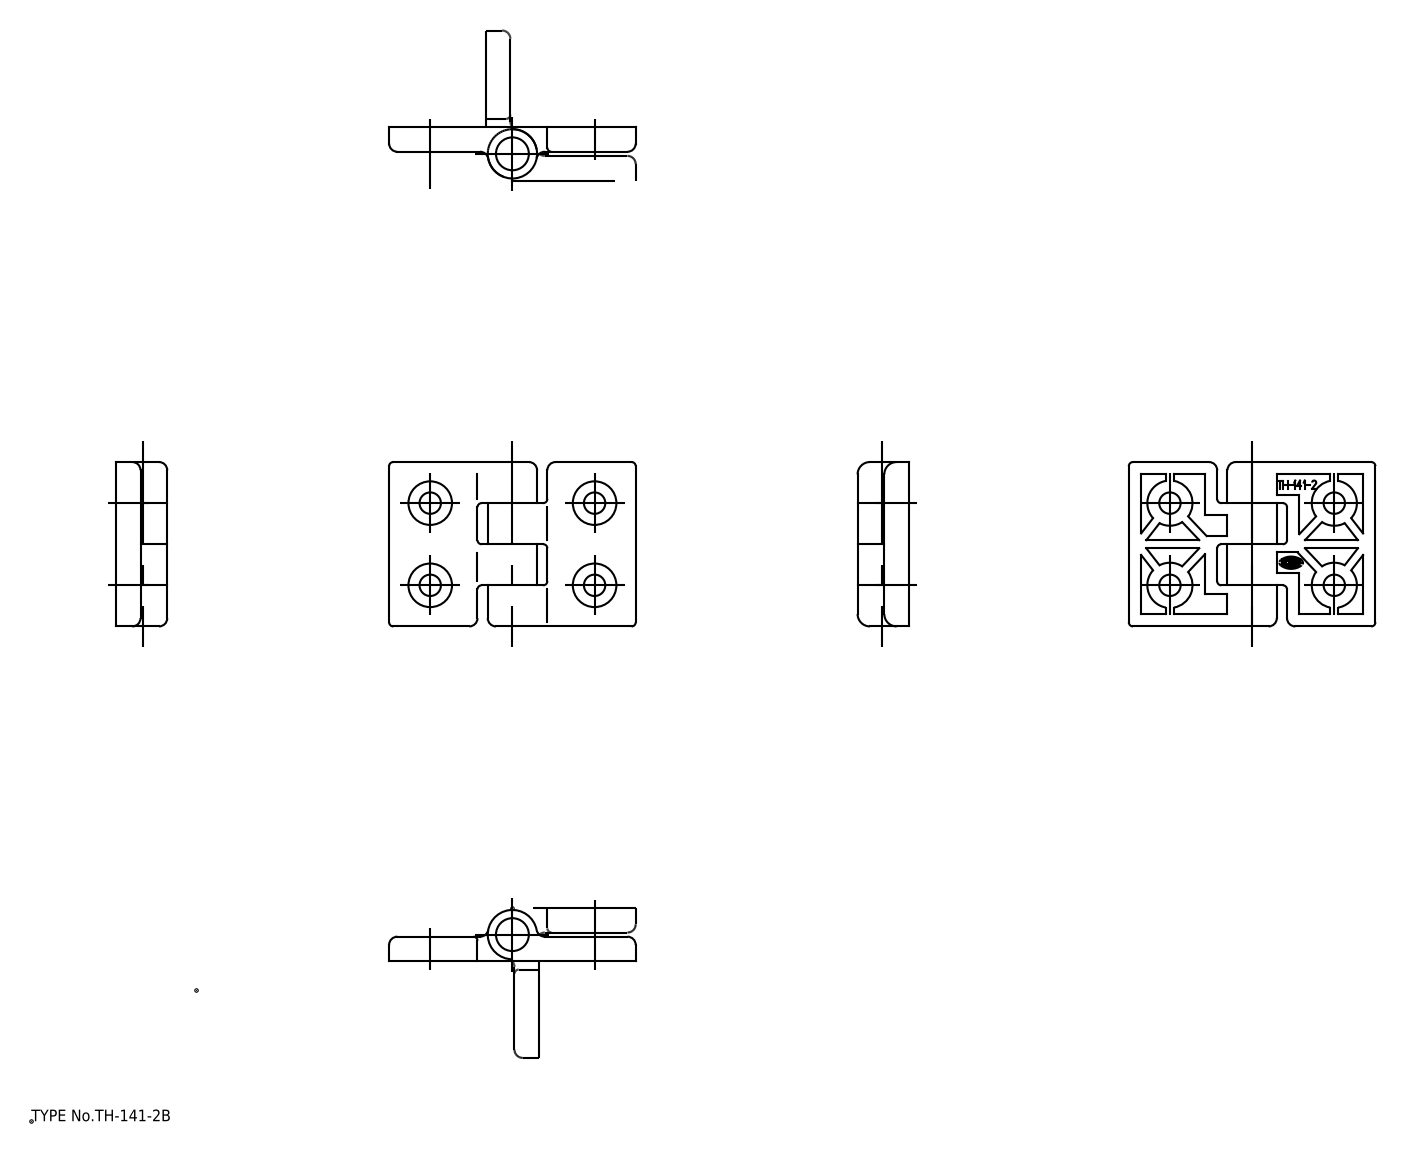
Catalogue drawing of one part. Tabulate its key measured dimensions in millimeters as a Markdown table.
| quantity | value |
| --- | --- |
| part name | cap; hinge pieces; shaft |
| STEP written by | spGate 19.8.4 (****-****-****-****) (AUTOMOTIVE_DESIGN) |
| units | millimeters |
| bodies | 5 solids, 198 faces (100 planar, 76 cylindrical, 22 other) |
| overall size | 60 × 40 × 12.5 |
| volume | 12 616 mm³ |
| surface area | 11 169 mm² |
| round holes (diameter × count) | 5.2 × 4, 10.6 × 4, 5 × 1, 6 × 1, 9.4 × 1 |
| round bosses / shafts (diameter × count) | 11 × 4, 12 × 1, 8 × 1 |
| partial cylindrical surfaces (radius × count) | 1 × 12, 2 × 8 |
| main face-to-face distances | 3, 6, 20, 10, 30, 17, 27, 2, 18.5, 38.5 |
| hole center spacings | 20, 40, 44.72 |
